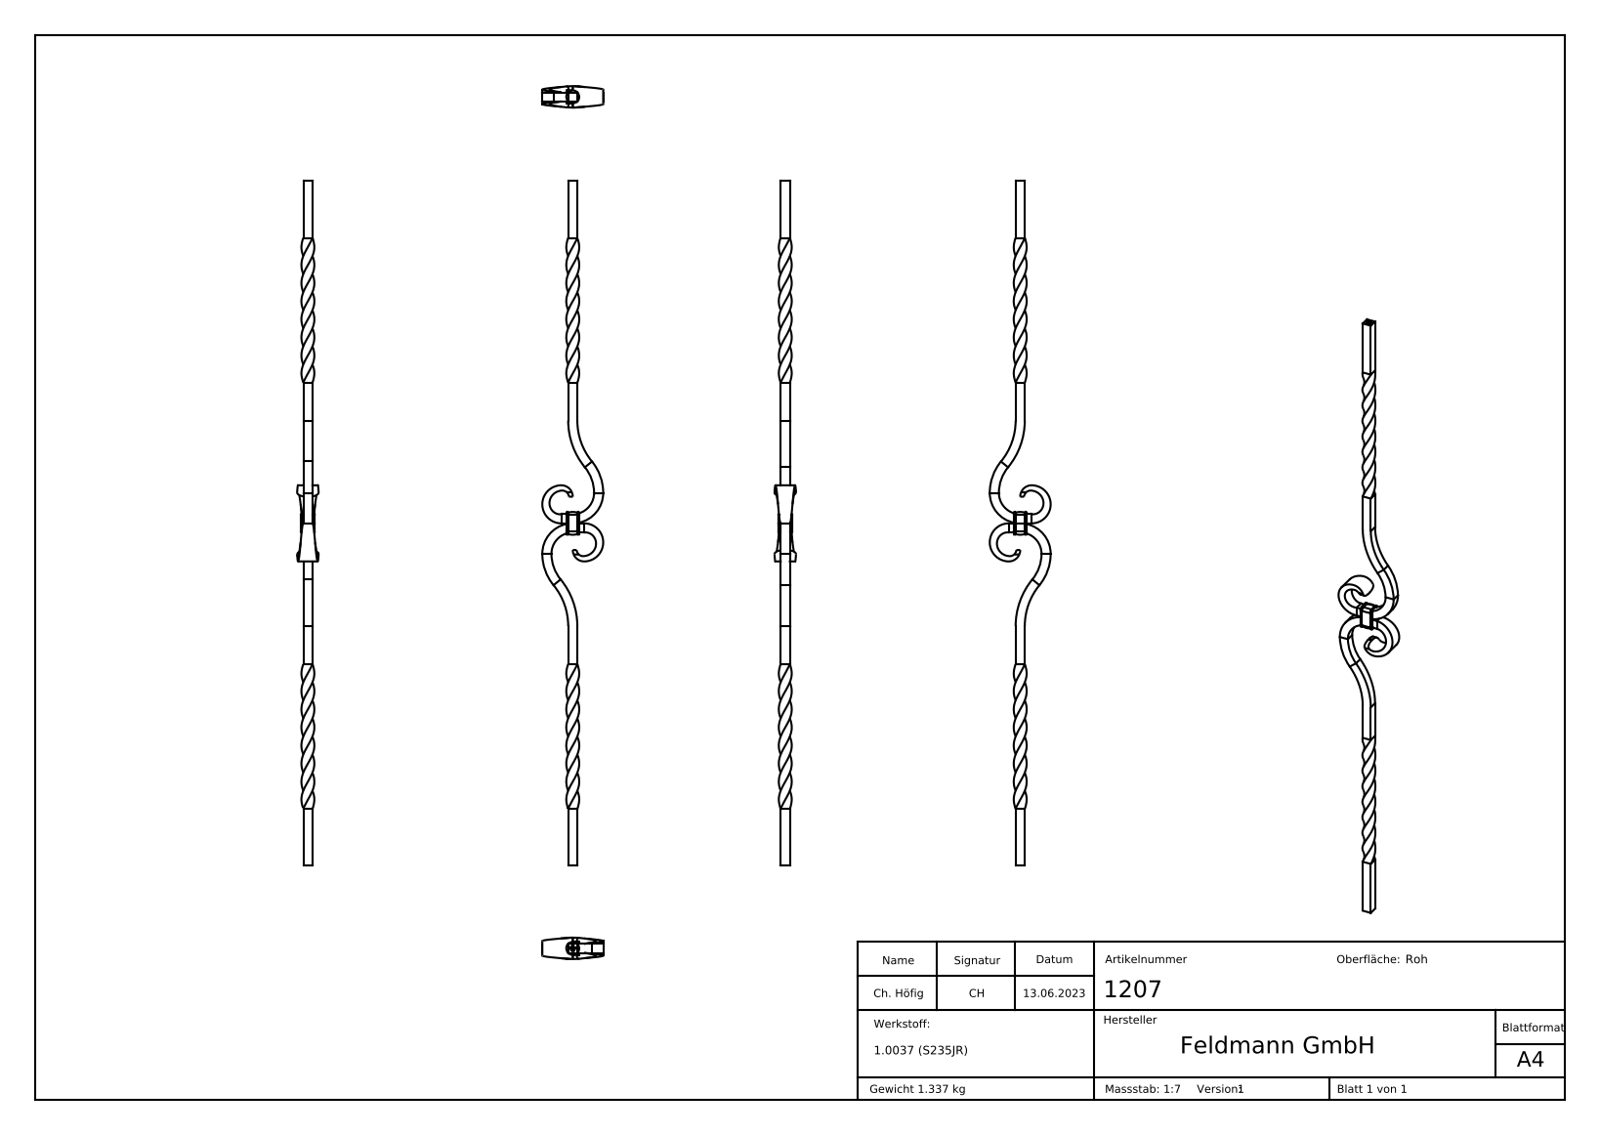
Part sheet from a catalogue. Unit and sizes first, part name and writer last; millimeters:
Units: millimetres
Overall size (bounding box): 900 × 80 × 28.26
Partial cylindrical surfaces — rounded edges, fillets, slot ends (radius × count): R0.5 ×24, R0.2 ×8, R1 ×4, R4 ×4, R20.14 ×4, R28 ×2, R40 ×2, R53 ×2
Main face-to-face distances: 12, 9, 21, 23, 24, 7, 14, 2, 30, 438
Volume: 185 517 mm³ · Surface area: 66 089 mm²
Bodies: 6 solids, 418 faces (204 planar, 69 cylindrical, 145 other)
Part name (STEP PRODUCT): 1207
STEP written by: SolidWorks 2018 (CONFIG_CONTROL_DESIGN)
